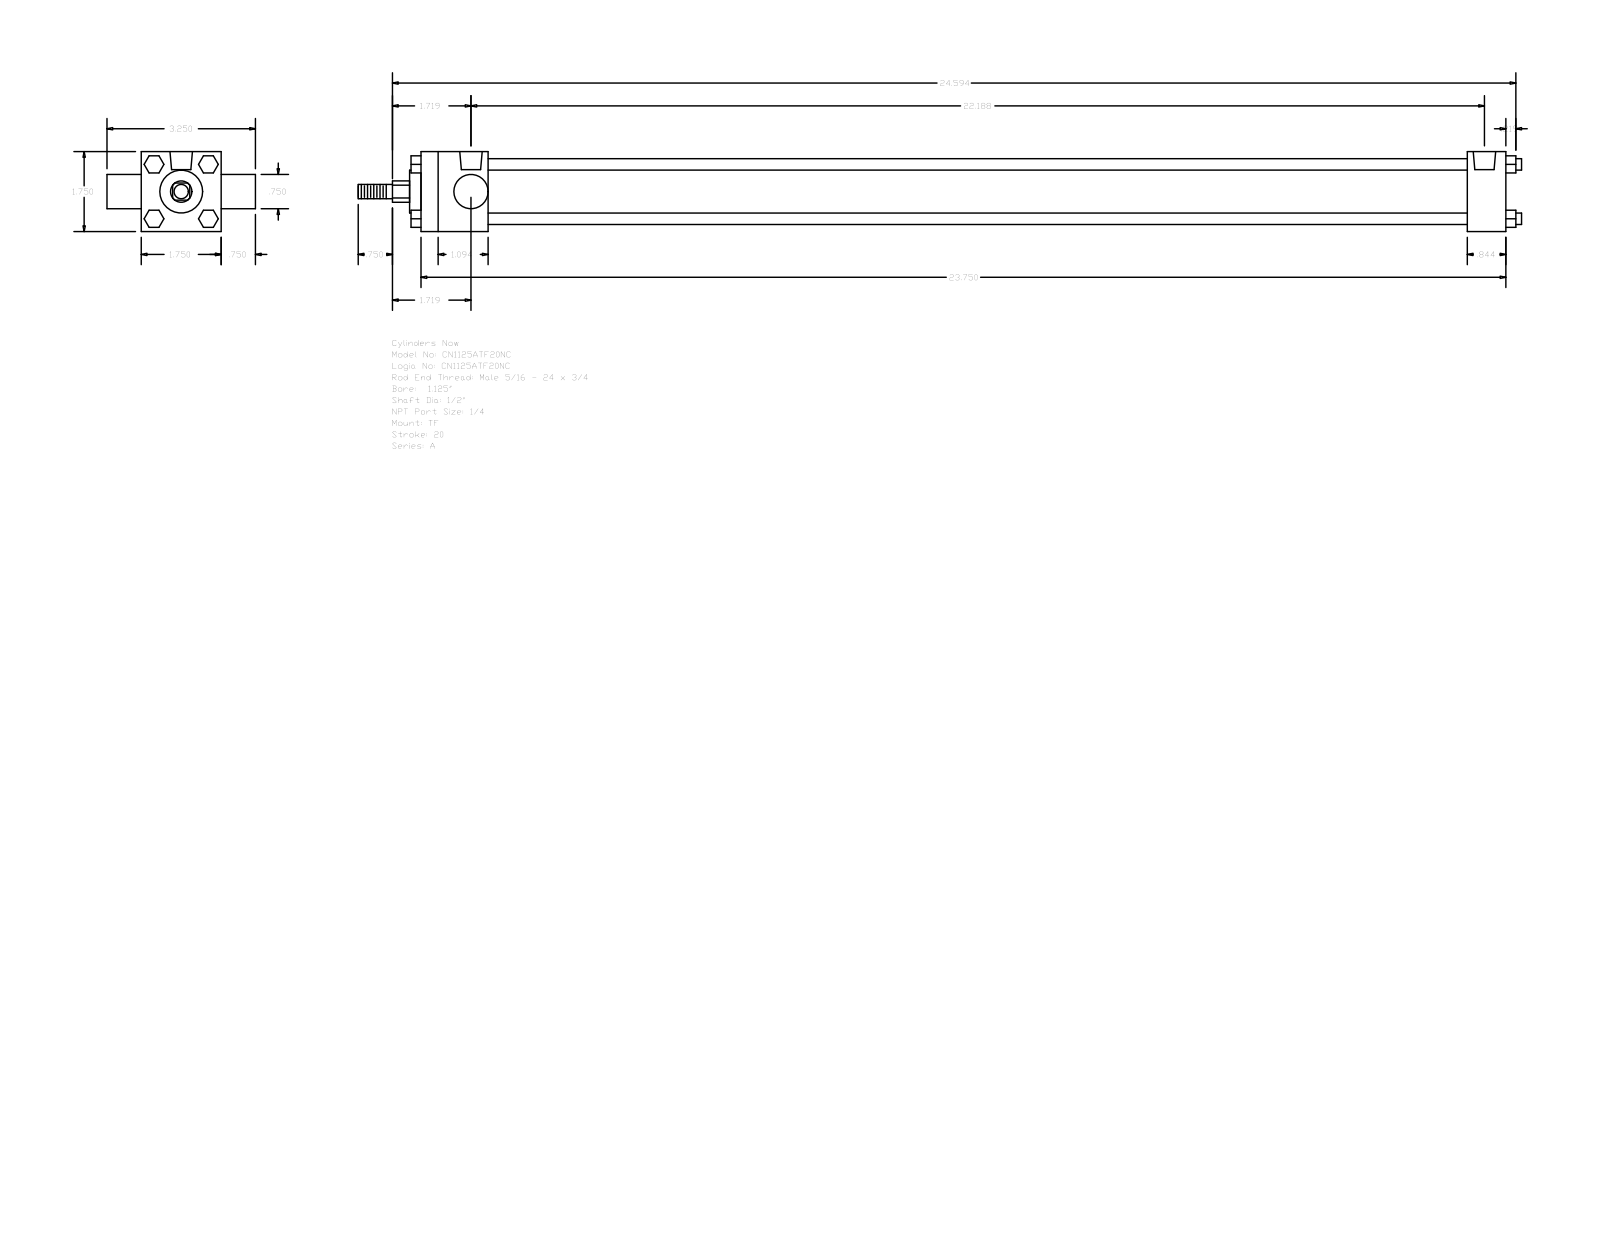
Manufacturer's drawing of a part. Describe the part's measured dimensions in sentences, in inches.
The part is named "A_TF__0112_0.5". Its 3-D file was written by "GSSL Pune (CONFIG_CONTROL_DESIGN)". It is 0 solids with 120 faces: 92 planar, 28 cylindrical and 0 other. Overall it measures 25.469 by 3.25 by 1.75 inches. Round holes: 3 of diameter 0.219, 2 of diameter 0.492. Round bosses or shafts: 4 of diameter 0.25, 1 of diameter 1.255, 1 of diameter 0.937, 1 of diameter 0.75, 1 of diameter 0.5, 1 of diameter 0.313. Partial cylindrical surfaces (rounded edges, fillets, slot ends): 1 of radius 0.234. The main face-to-face distances are 1.75, 23.75, 22.906, 0.844, 1.469, 21.437, 22.281, 0.75, 2.5, 0.375. The hole center spacings are 0.062, 0.063, 22.063, 22.125, 22.125, 22.187.
